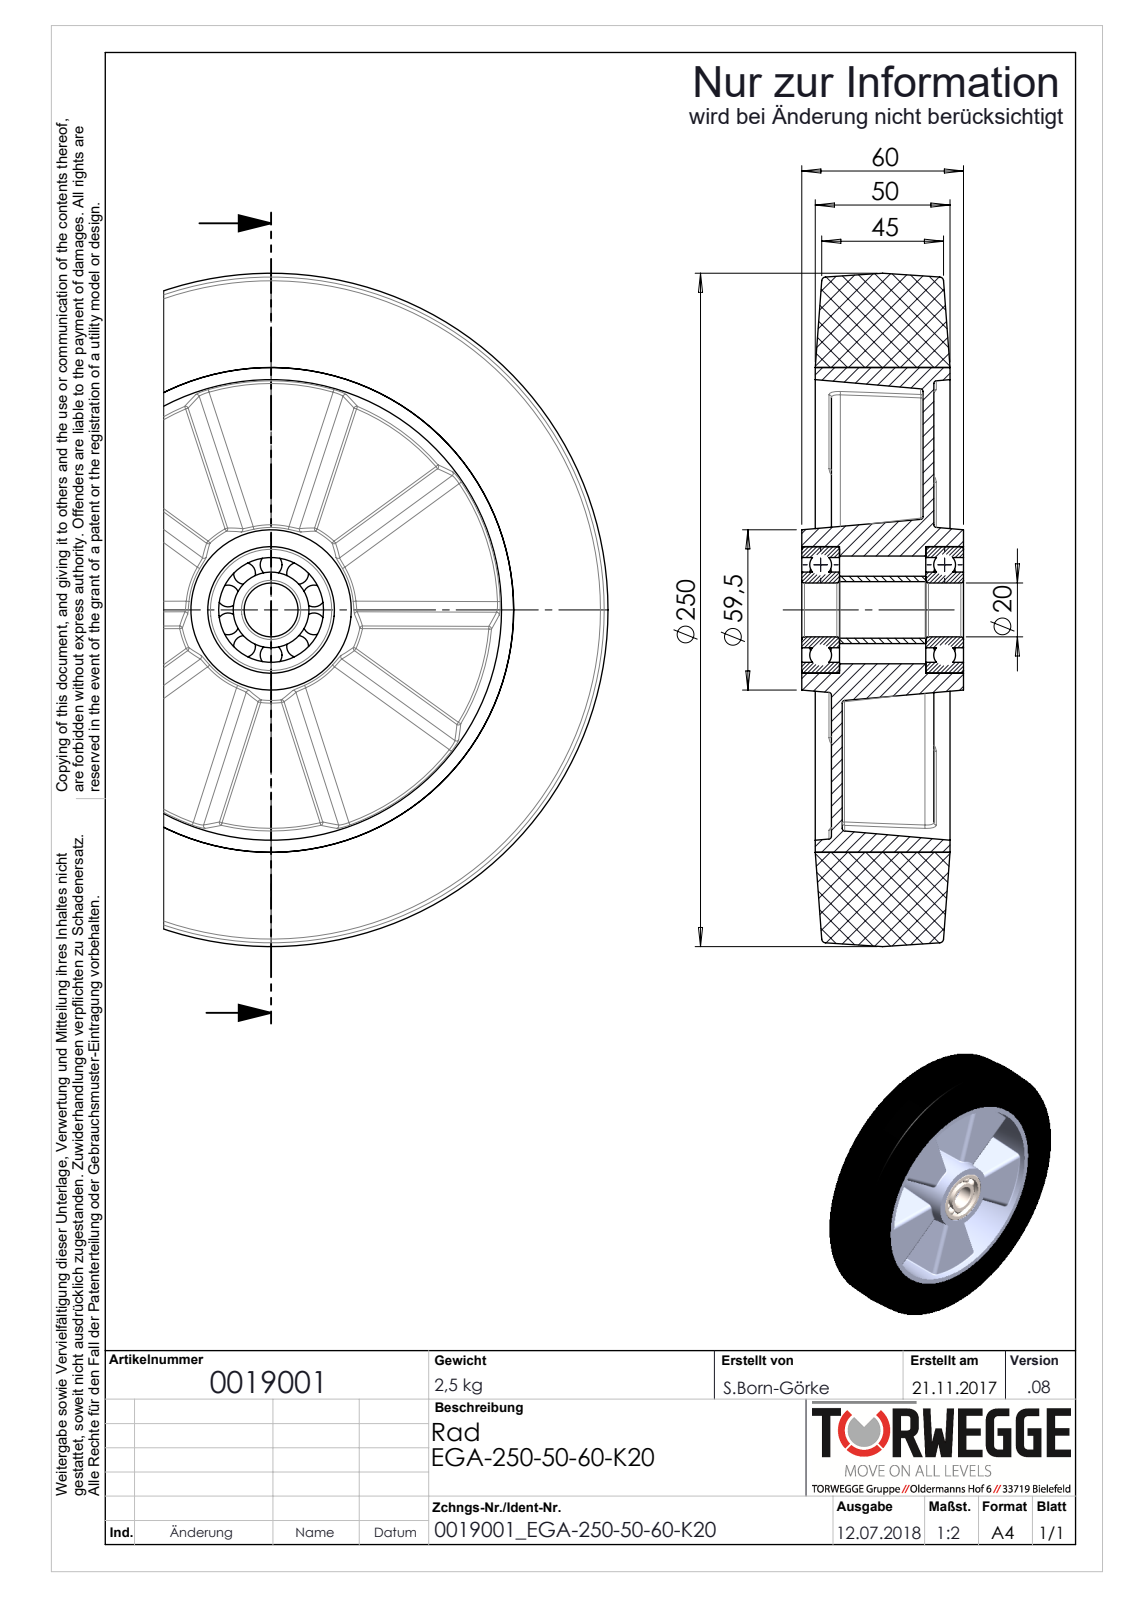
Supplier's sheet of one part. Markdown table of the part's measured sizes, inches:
| quantity | value |
| --- | --- |
| part name | 0019001_EGA-250-50-60-K20 |
| STEP written by | SolidWorks 2016 (AUTOMOTIVE_DESIGN) |
| units | inches |
| bodies | 9 solids, 390 faces (64 planar, 94 cylindrical, 232 other) |
| overall size | 9.843 × 9.843 × 2.362 |
| volume | 96.11 in³ |
| surface area | 423.2 in² |
| round holes (diameter × count) | 0.787 × 1, 0.827 × 1, 1.106 × 1, 1.531 × 1, 1.575 × 1, 1.85 × 1, 7.087 × 1 |
| round bosses / shafts (diameter × count) | 0.984 × 1 |
| partial cylindrical surfaces (radius × count) | 0.039 × 20, 0.157 × 20 |
| main face-to-face distances | 1.339, 0.157, 1.496, 0.261, 0.26, 1.181, 0.236, 0.394, 1.575, 1.732 |
